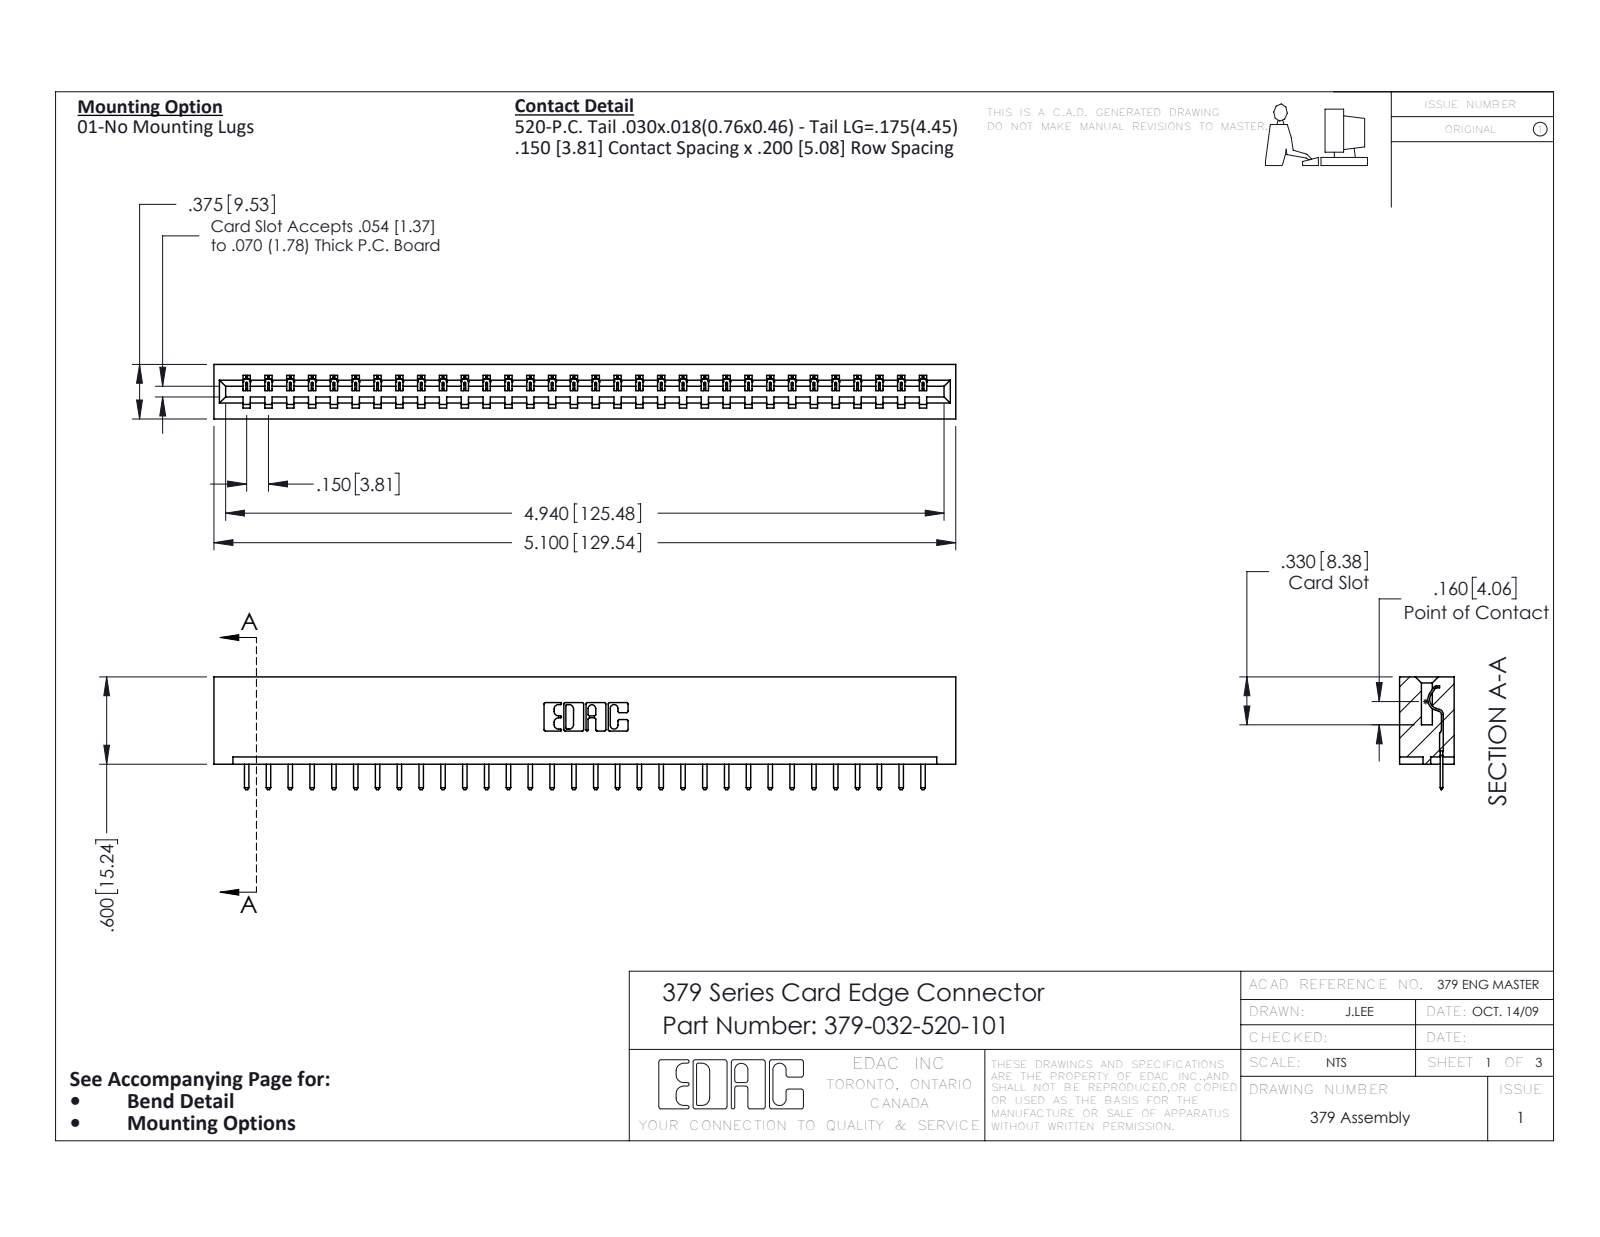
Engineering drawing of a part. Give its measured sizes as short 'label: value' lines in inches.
name: 345-292-001_345-293-120; 379 Part_Lugless; 379-032-520-101
written by: SolidWorks 2016 (CONFIG_CONTROL_DESIGN)
unit: in
bodies: 33 solids, 2090 faces (1474 planar, 616 cylindrical, 0 other)
size: 5.1 × 0.775 × 0.375
volume: 0.862 in³; area: 21.75 in²
rounds: 66× R0.01, 64× R0.006, 22× R0.01, 6× R0.007, 6× R0.031, 3× R0.026, 1× R0.014, 1× R0.022
face distances: 0.3, 0.075, 0.375, 0.225, 0.6, 0.15, 0.55, 0.45, 0.15, 0.15
